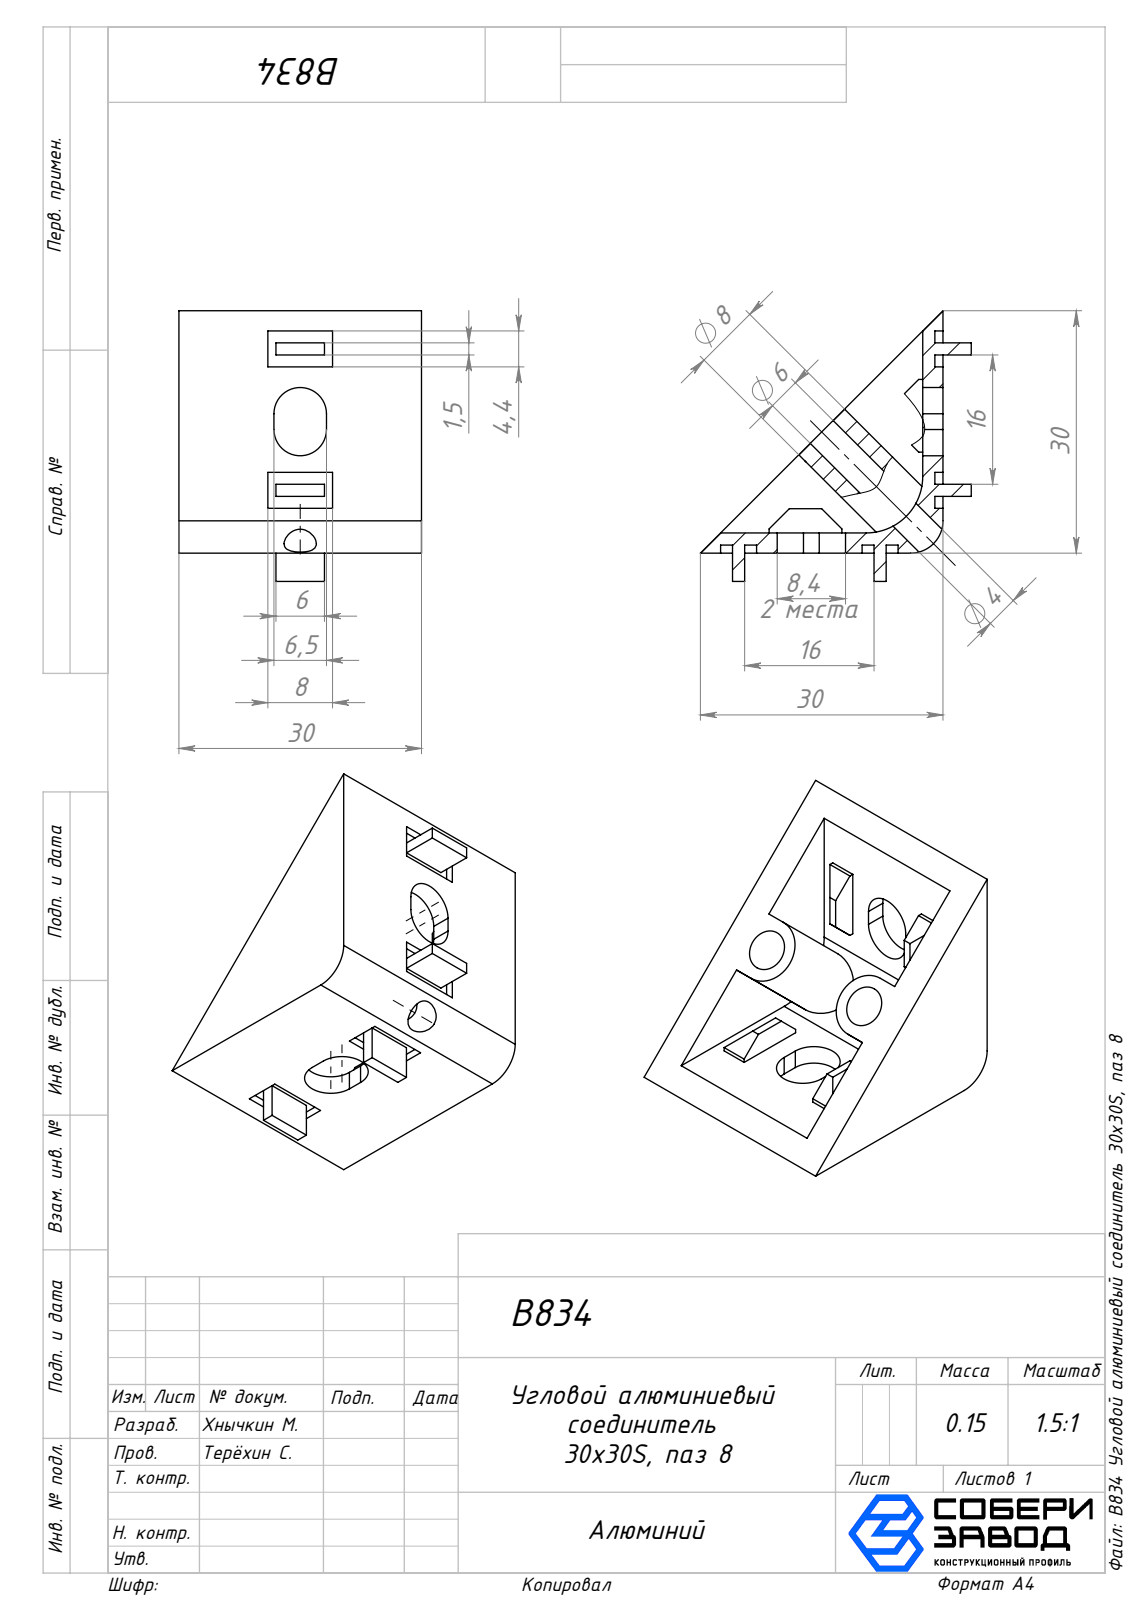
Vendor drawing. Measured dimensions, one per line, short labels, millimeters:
name: B834 Угловой алюминиевый соединитель 30х30S, паз 8
written by: SolidWorks 2025 (AUTOMOTIVE_DESIGN)
unit: mm
bodies: 1 solid, 107 faces (91 planar, 16 cylindrical, 0 other)
size: 33.5 × 33.5 × 30
volume: 7 431 mm³; area: 5 990 mm²
holes: 2× ⌀5, 1× ⌀4
rounds: 4× R3.25, 3× R4, 1× R7
face distances: 2.5, 30, 4, 26, 1.5, 22, 9, 1, 8, 6.03
hole spacings: 8.5, 17
